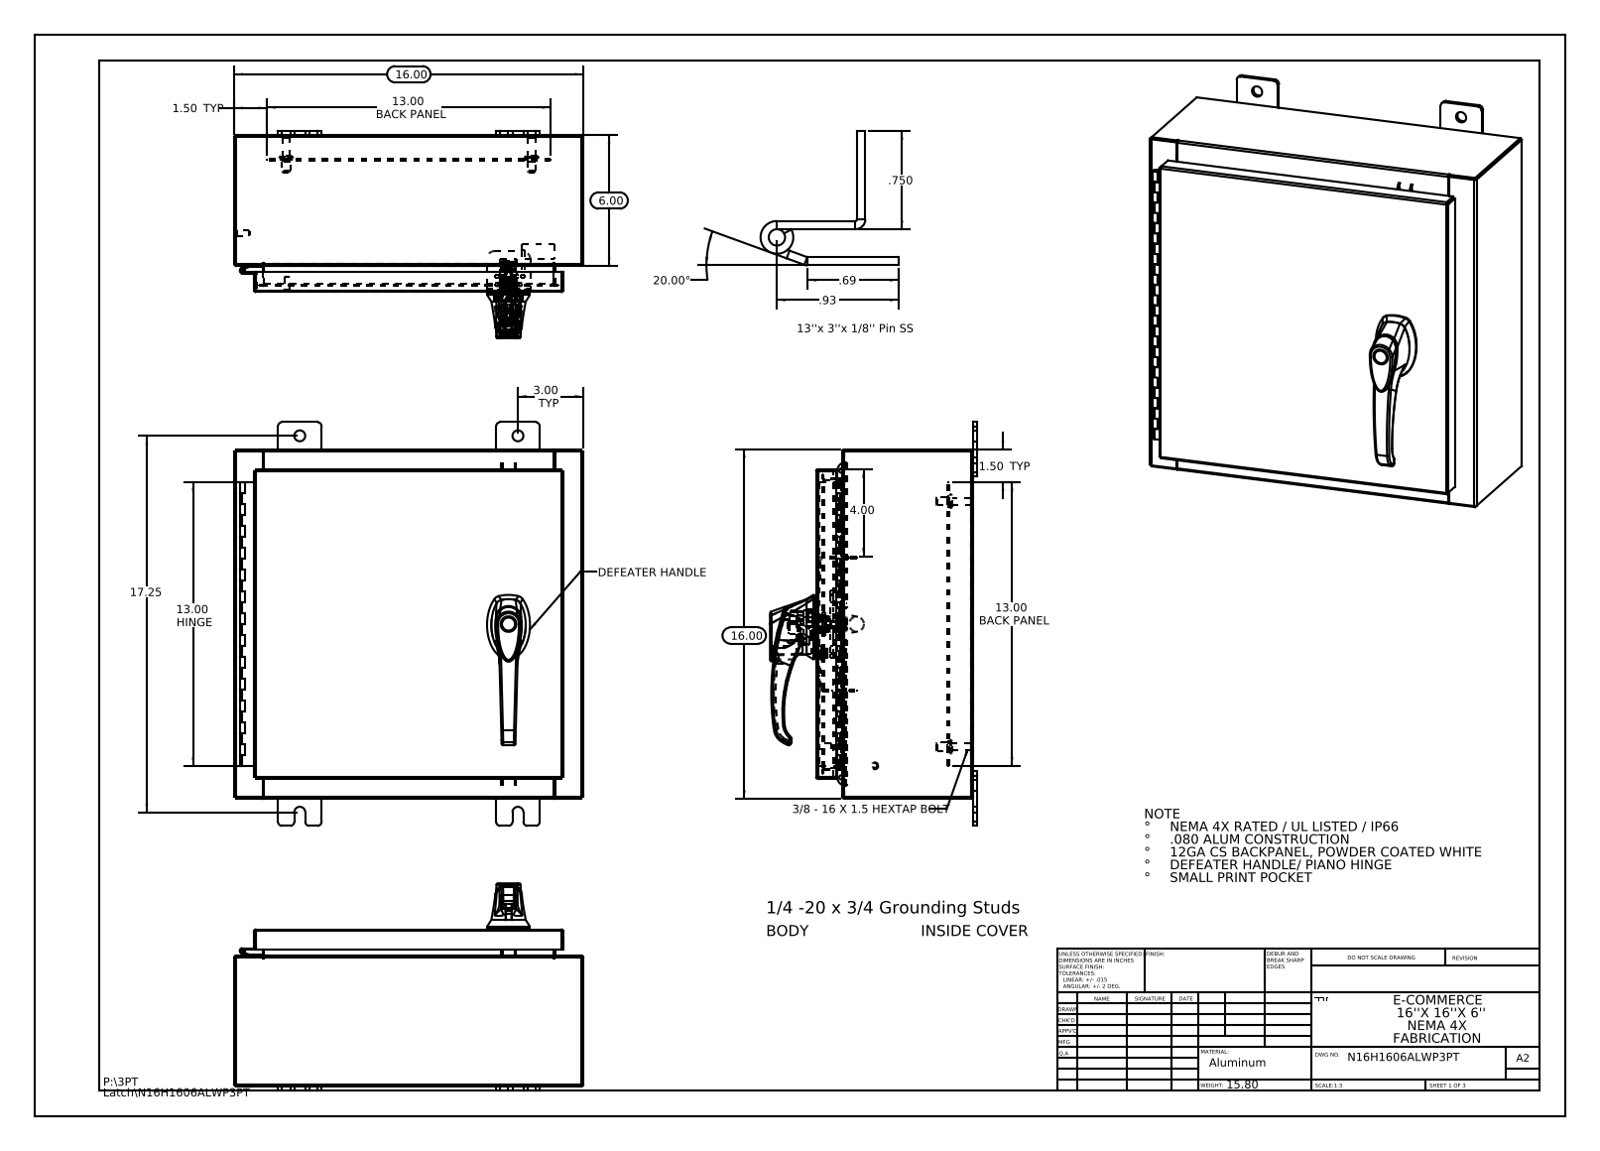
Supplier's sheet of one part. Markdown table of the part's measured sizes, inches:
| quantity | value |
| --- | --- |
| part name | N16H1606ALWP3PT 125 Pin Hinge; NMP-SS-RODGUIDES; 00005309_G26103101; N16H1606ALWP3PT Hinge Cover Side (+8 more) |
| STEP written by | SolidWorks 2013 (CONFIG_CONTROL_DESIGN) |
| units | inches |
| bodies | 37 solids, 2290 faces (775 planar, 817 cylindrical, 698 other) |
| overall size | 18.5 × 16 × 9.495 |
| volume | 108.8 in³ |
| surface area | 2 664 in² |
| round holes (diameter × count) | 0.5 × 8, 0.25 × 4, 0.138 × 3, 0.161 × 3, 0.079 × 2, 0.203 × 2, 0.313 × 2, 0.437 × 2, 0.125 × 1, 0.125 × 1, 0.197 × 1, 0.276 × 1 |
| round bosses / shafts (diameter × count) | 0.625 × 4, 0.375 × 4, 0.33 × 4, 0.157 × 4, 0.14 × 4, 0.315 × 3, 0.236 × 3, 1.181 × 1 |
| partial cylindrical surfaces (radius × count) | 0.118 × 37, 0.006 × 33, 0.19 × 24, 0.013 × 20, 0.088 × 18, 0.039 × 15, 0.028 × 12, 0.008 × 6 |
| main face-to-face distances | 0.075, 7.126, 15.925, 7.051, 7.201, 15.85, 16, 1, 0.104, 1.075 |
| hole center spacings | 3.708, 0.295, 0.625, 0.841, 1.25, 1.313, 1.32, 1.484 |
